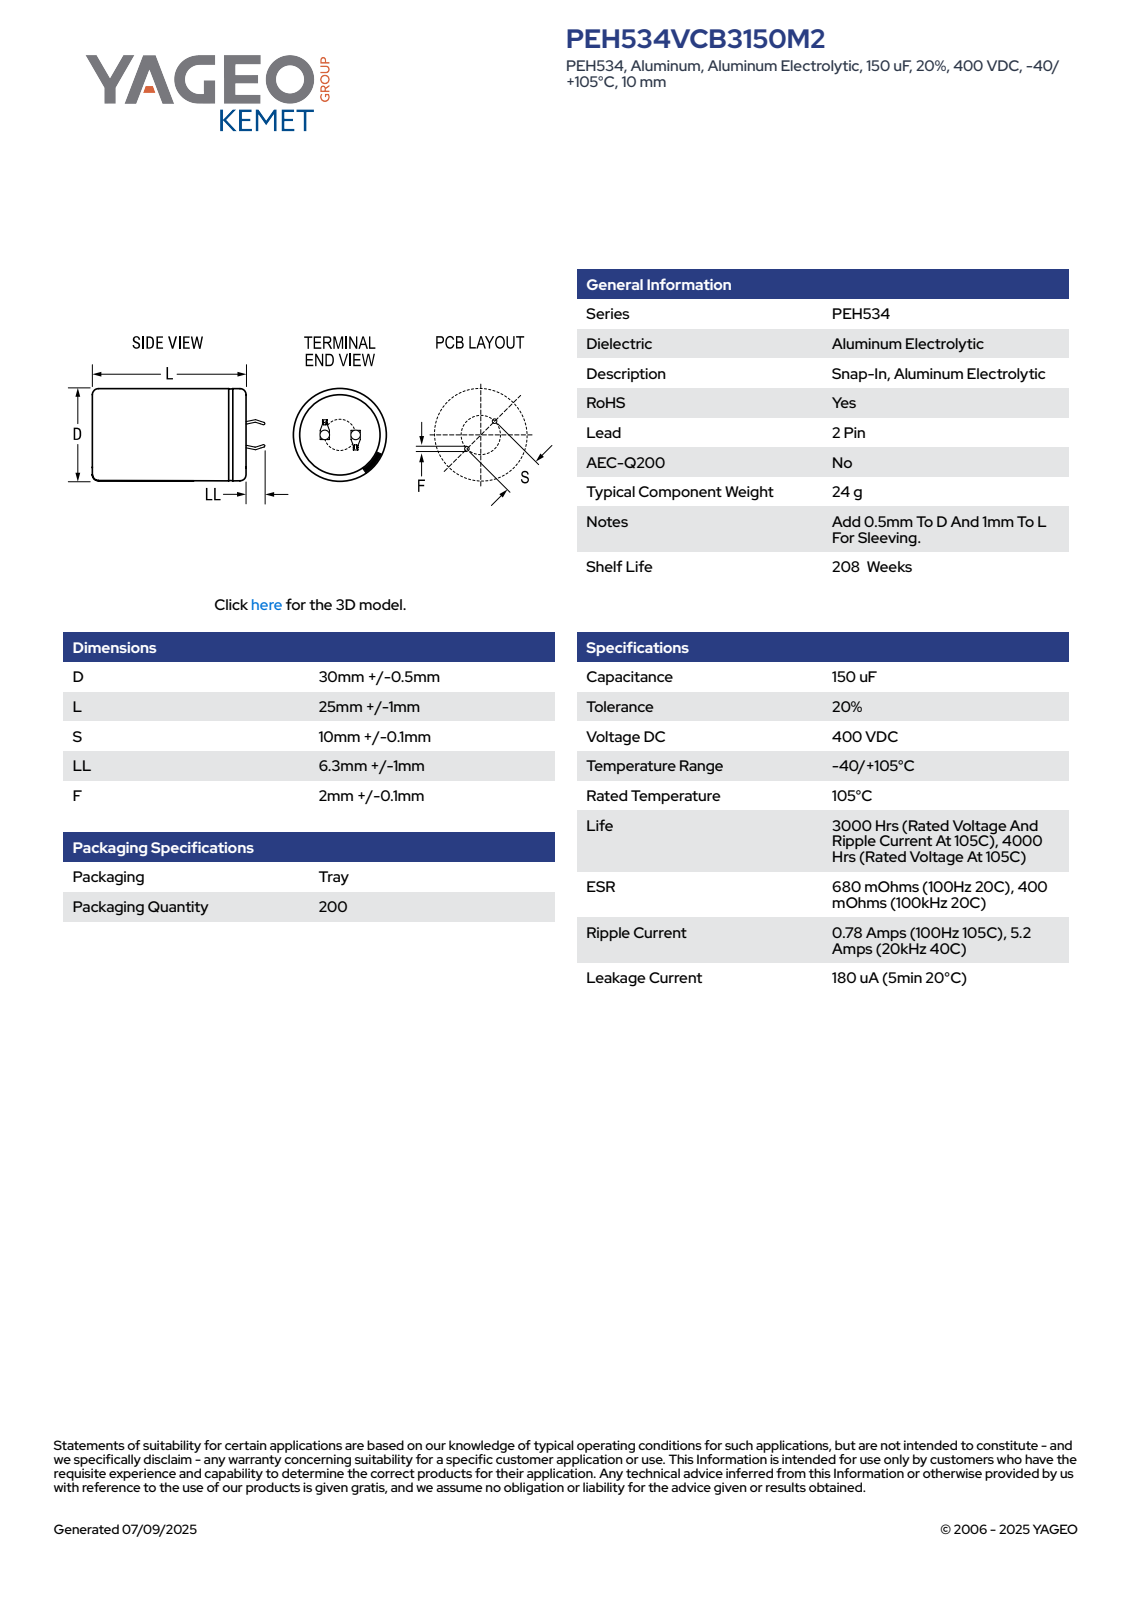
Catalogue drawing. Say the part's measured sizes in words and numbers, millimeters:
The part is named "CARS_K2P_30X25_D30.5L26S10LL7.3F2.1". Its 3-D file was written by "SolidWorks 2014 (AUTOMOTIVE_DESIGN)". It is 1 solid with 100 faces: 52 planar, 9 cylindrical and 39 other. Overall it measures 33.29 by 30.5 by 30.5 millimeters. Its volume is 18 679 cubic millimeters and its surface area 3 964 square millimeters. Round holes: 1 of diameter 26.99. Round bosses or shafts: 1 of diameter 30.5. Partial cylindrical surfaces (rounded edges, fillets, slot ends): 1 of radius 15.24. The main face-to-face distances are 25.99, 0.6, 26.49, 0.5, 7.08, 7.64, 0.75, 1.35, 7.68, 6.48.
